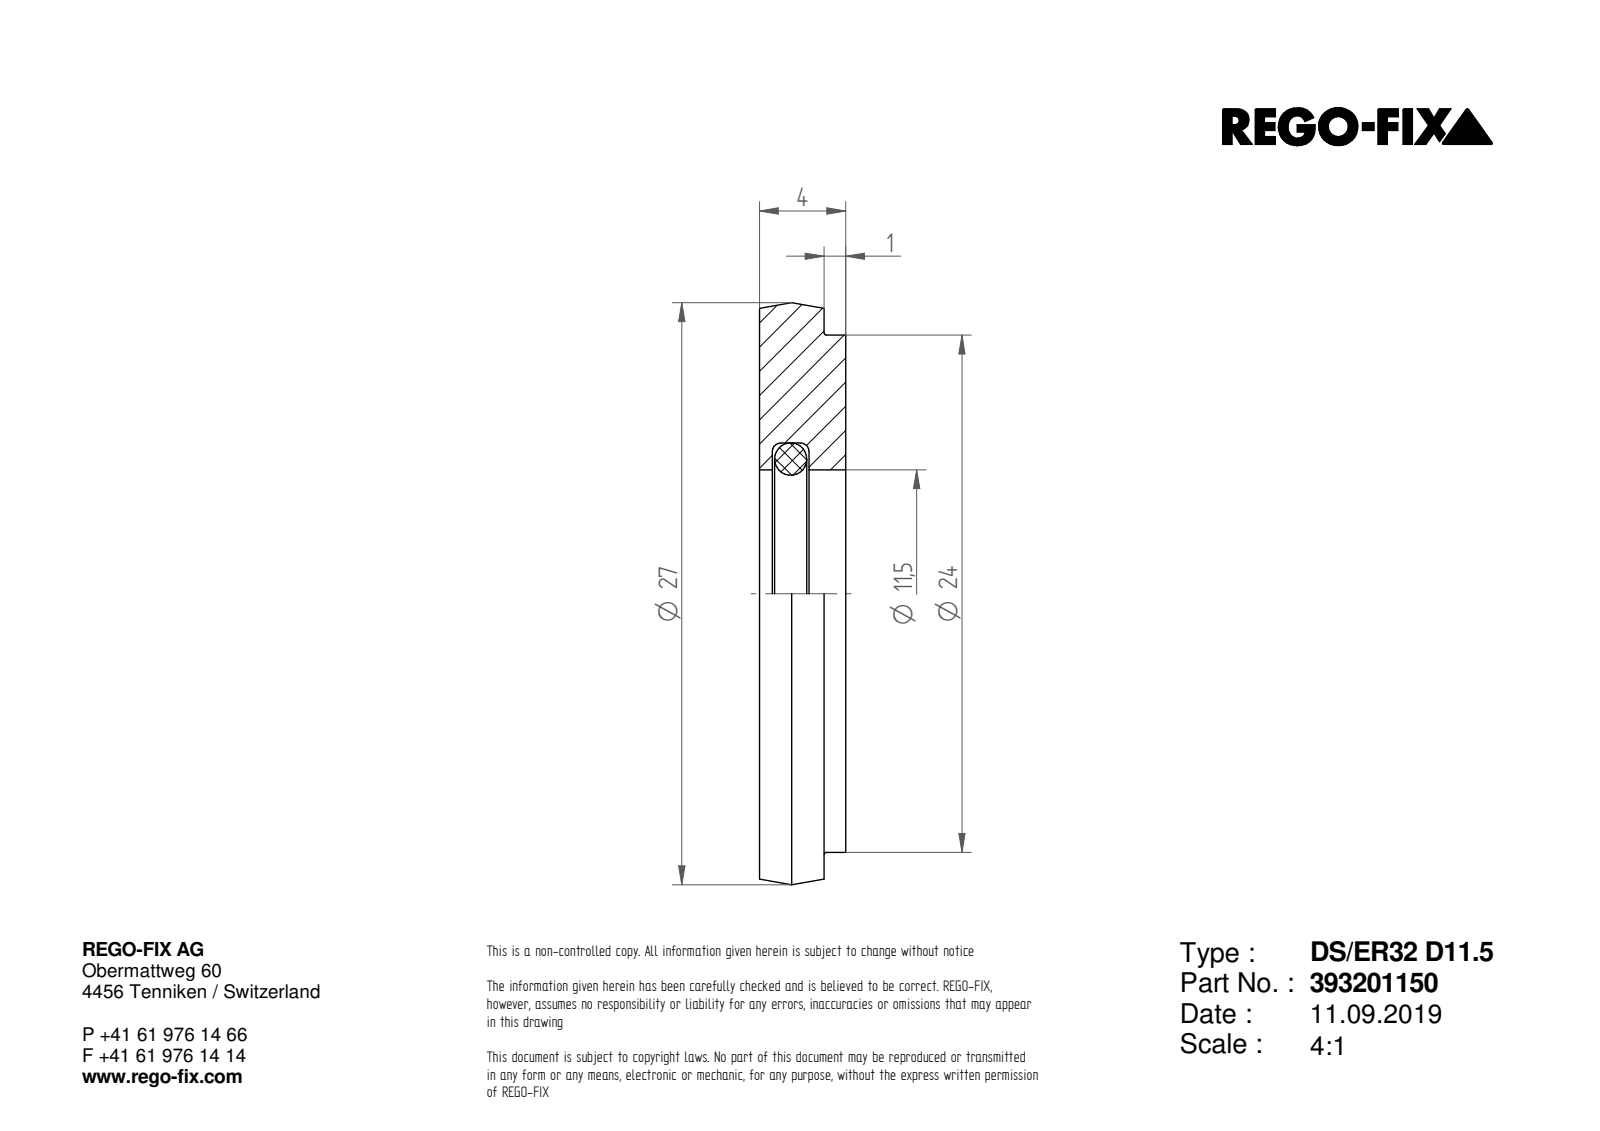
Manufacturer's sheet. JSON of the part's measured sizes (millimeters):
{"part_name": "NOCUT", "step_written_by": "SIEMENS PLM Software Solid Edge ST10 (AUTOMOTIVE_DESIGN)", "units": "millimeters", "bodies": {"solids": 1, "faces": 7, "planar": 3, "cylindrical": 3, "other": 1}, "overall_size": [27, 27, 4], "volume_mm3": 1755, "surface_area_mm2": 1409, "round_holes": [[11.5, 1]], "round_bosses_or_shafts": [[27, 1], [24, 1]], "face_to_face_distances": [4, 1, 3]}
